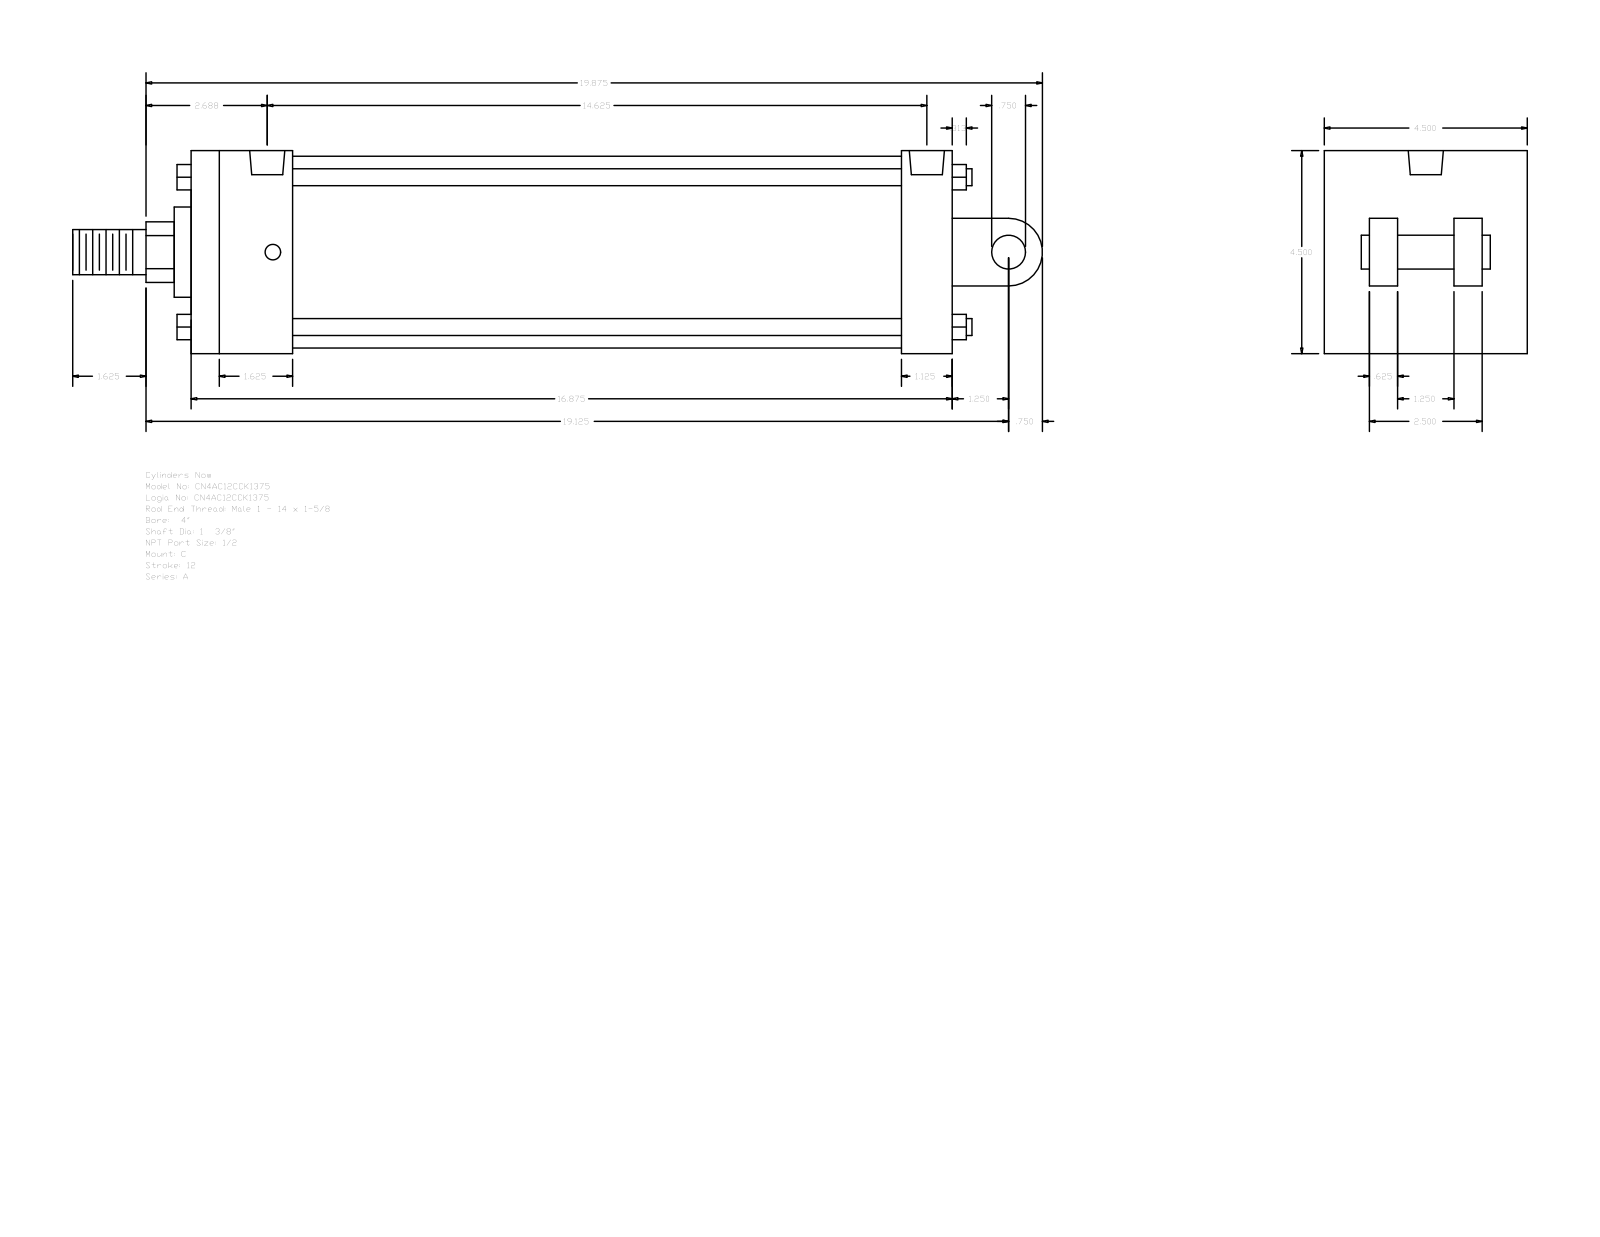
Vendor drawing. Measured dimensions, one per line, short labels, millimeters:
name: A_C__0400_1.375
written by: GSSL Pune (CONFIG_CONTROL_DESIGN)
unit: mm
bodies: 0 solids, 135 faces (102 planar, 33 cylindrical, 0 other)
size: 546.1 × 114.3 × 114.3
holes: 4× ⌀8.73, 2× ⌀19.77
bosses: 4× ⌀9.53, 1× ⌀107.95, 1× ⌀50.8, 1× ⌀34.92, 1× ⌀25.4, 1× ⌀19.05
rounds: 1× R17.06, 1× R19.05
face distances: 114.3, 428.62, 57.15, 73.03, 400.05, 28.57, 342.9, 371.47, 41.27, 25.4
hole spacings: 3.18, 365.12, 368.3, 371.48
